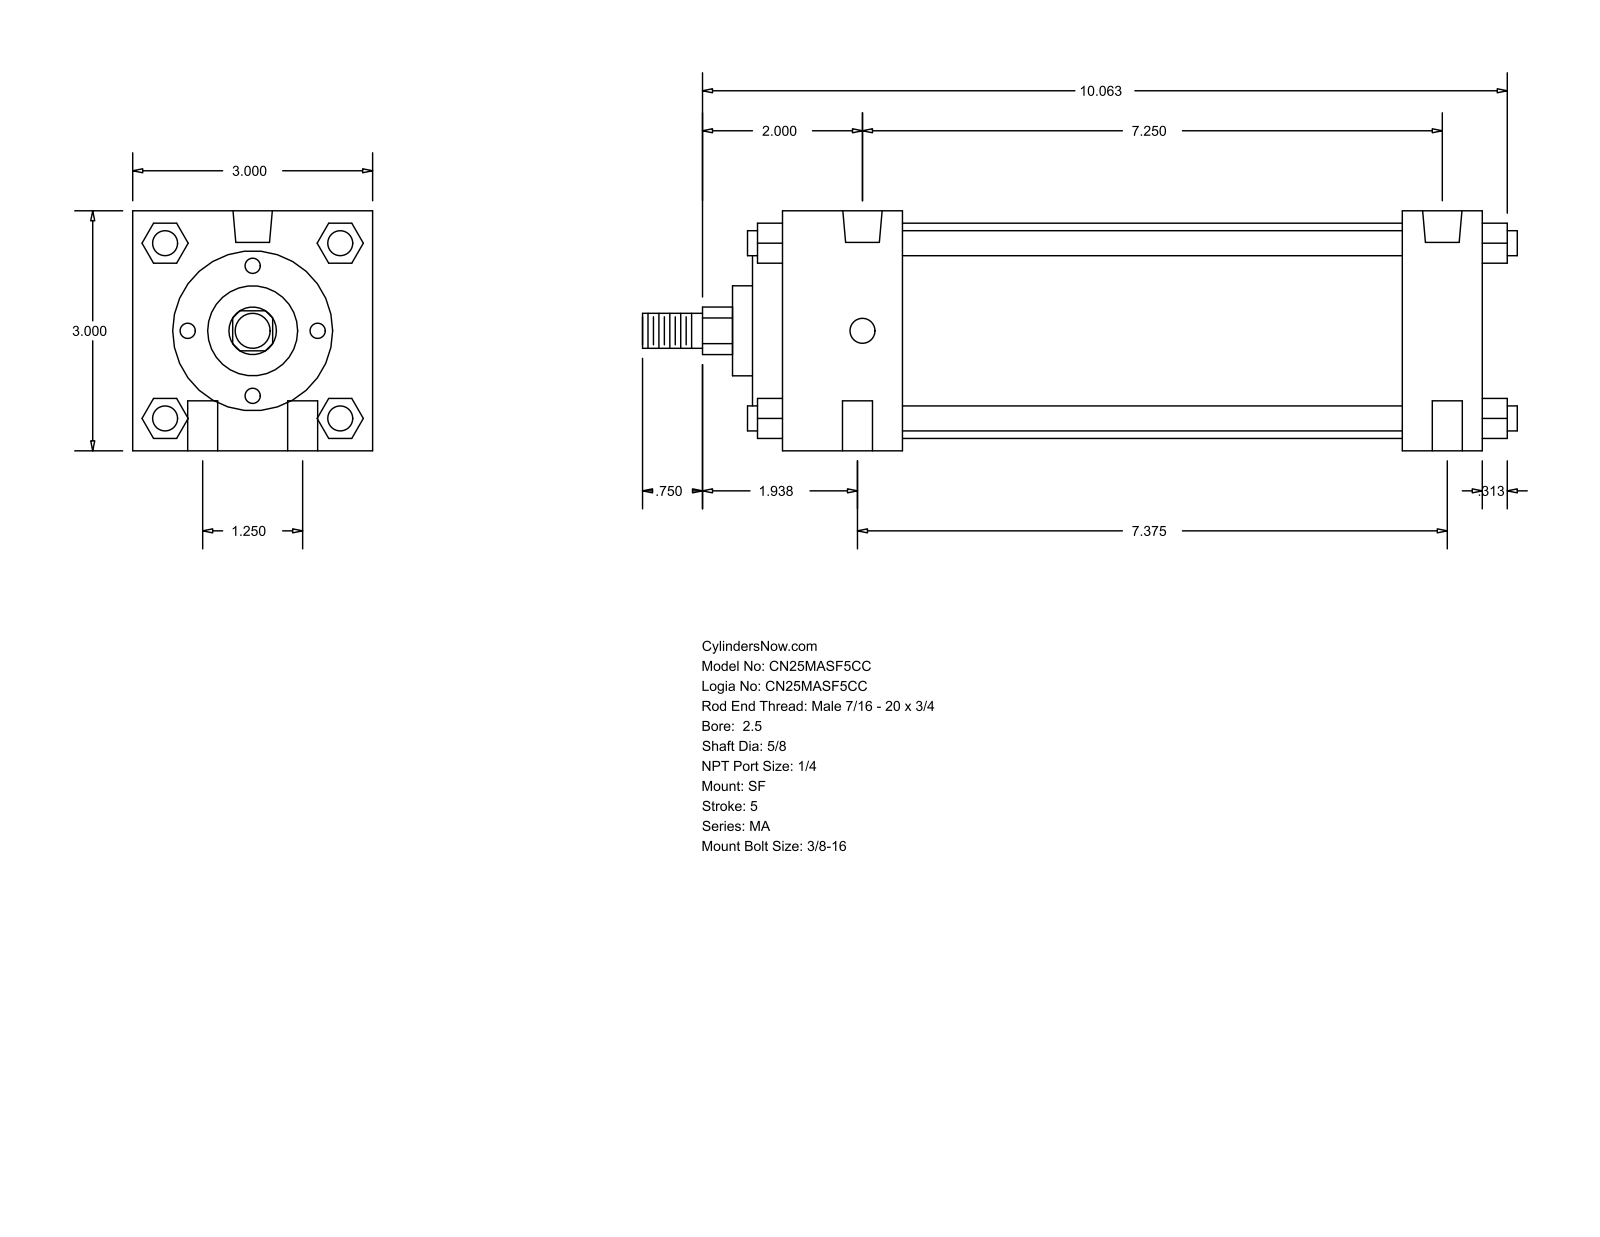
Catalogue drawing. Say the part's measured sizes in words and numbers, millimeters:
The part is named "MA_SF__0250_0.625". Its 3-D file was written by "GSSL Pune (CONFIG_CONTROL_DESIGN)". It is 0 solids with 126 faces: 95 planar, 31 cylindrical and 0 other. Overall it measures 277.81 by 76.2 by 76.2 millimeters. Round holes: 4 of diameter 9.53, 2 of diameter 7.94, 2 of diameter 12.49. Round bosses or shafts: 4 of diameter 7.94, 1 of diameter 68.33, 1 of diameter 50.8, 1 of diameter 28.57, 1 of diameter 15.88, 1 of diameter 11.11. Partial cylindrical surfaces (rounded edges, fillets, slot ends): 1 of radius 7.54. The main face-to-face distances are 76.2, 222.25, 25.4, 196.85, 38.1, 158.75, 184.15, 12.7, 9.52, 47.62. The hole center spacings are 15.96, 186.42, 31.76, 184.15, 187.33, 190.
